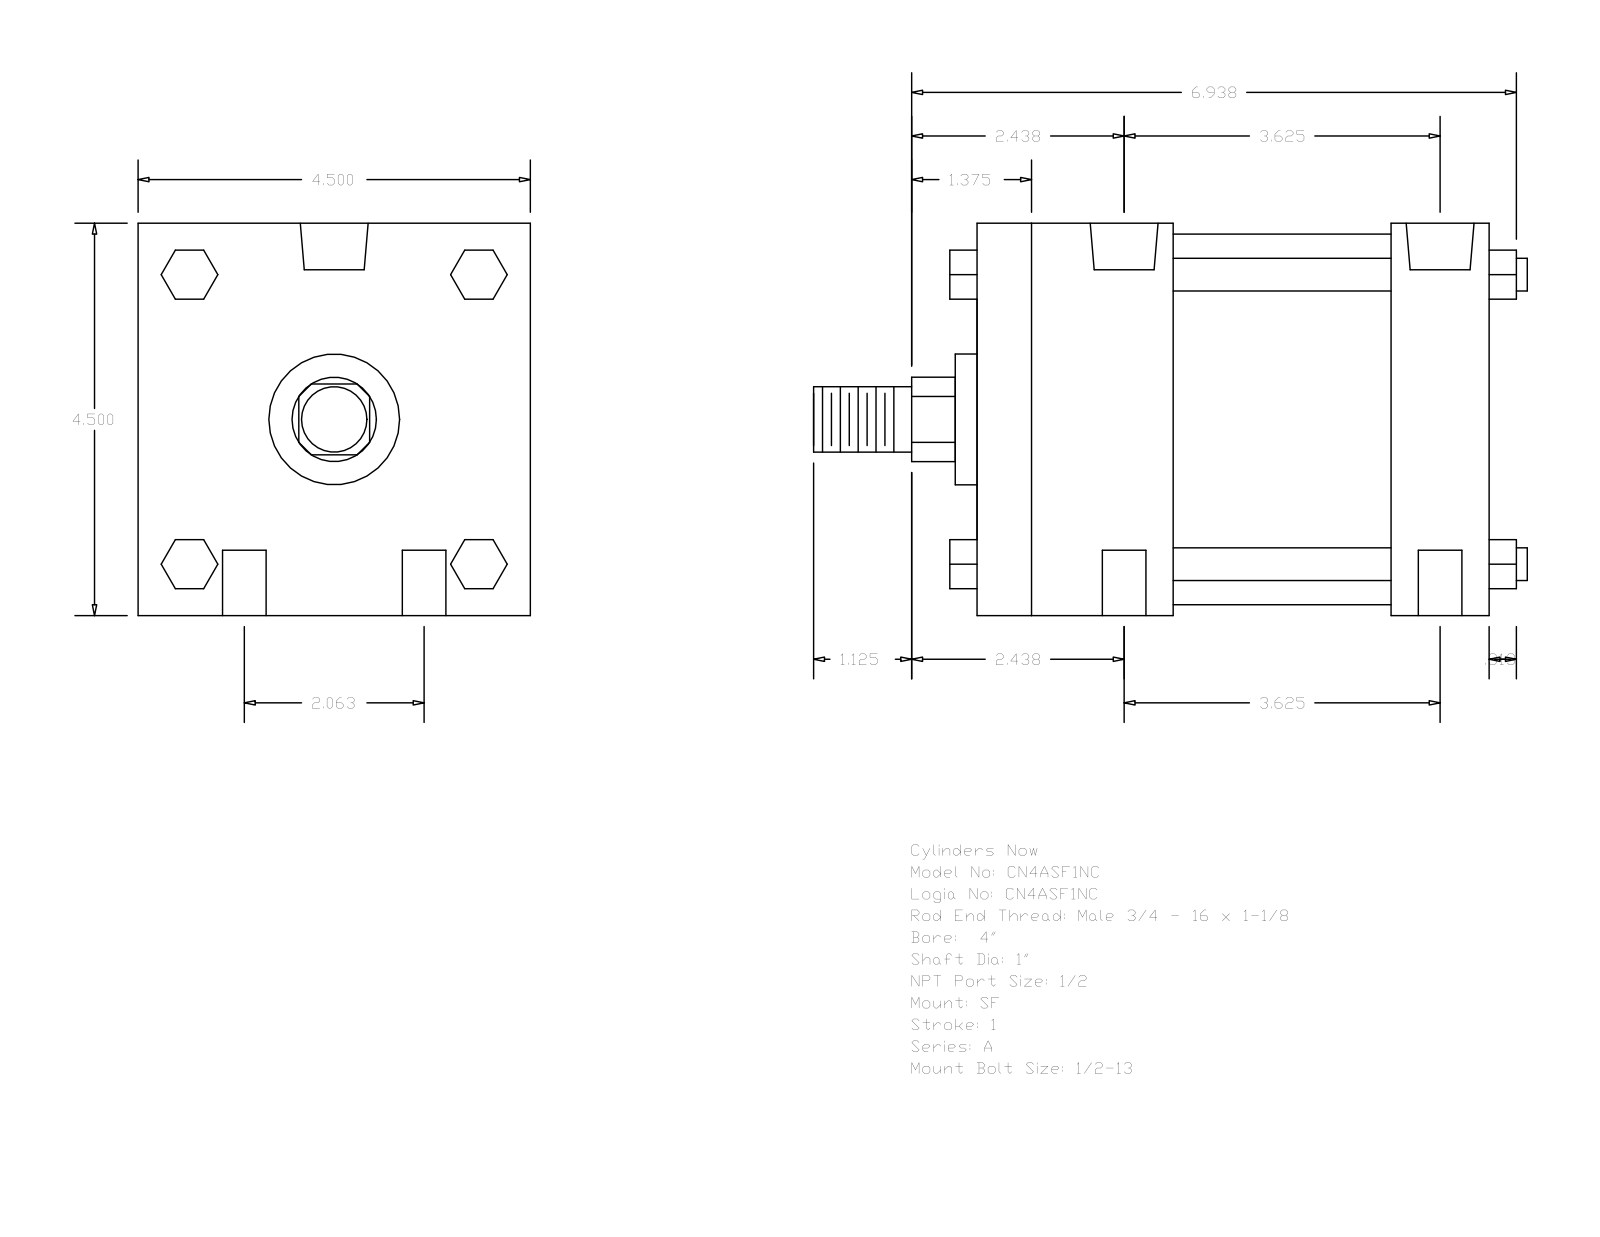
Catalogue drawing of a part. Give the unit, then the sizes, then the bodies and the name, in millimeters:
Units: millimetres
Overall size (bounding box): 207.96 × 114.3 × 114.3
Round holes (diameter × count): ⌀12.7 ×4, ⌀8.73 ×2, ⌀19.77 ×2
Round bosses / shafts (diameter × count): ⌀9.53 ×4, ⌀107.95 ×1, ⌀38.1 ×1, ⌀25.4 ×1, ⌀19.05 ×1
Partial cylindrical surfaces — rounded edges, fillets, slot ends (radius × count): R12.29 ×1
Main face-to-face distances: 114.3, 149.23, 63.5, 120.65, 28.58, 57.15, 92.08, 14.29, 42.16, 73.03
Hole centre spacings: 26.19, 95.73, 92.08, 52.38, 105.94, 85.72
Bodies: 0 solids, 124 faces (94 planar, 30 cylindrical, 0 other)
Part name (STEP PRODUCT): A_SF__0400_1
STEP written by: GSSL Pune (CONFIG_CONTROL_DESIGN)
